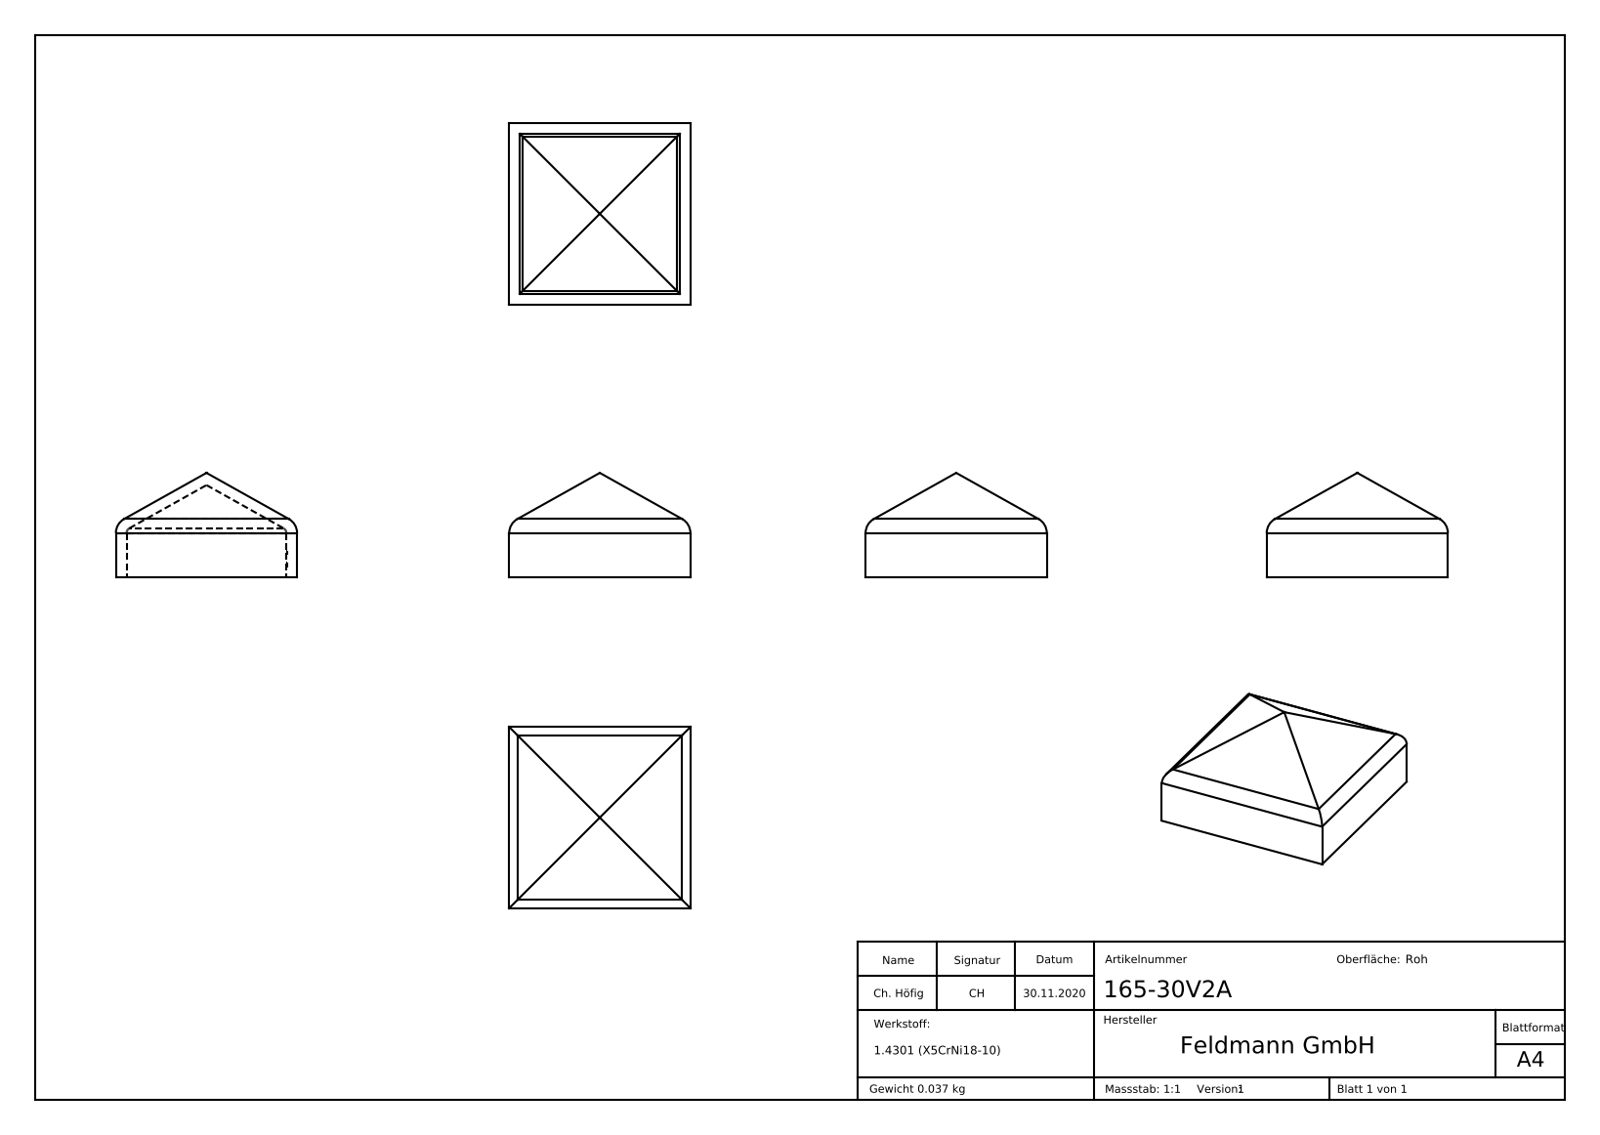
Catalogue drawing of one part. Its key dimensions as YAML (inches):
part_name: "165-30V2A"
step_written_by: "SolidWorks 2018 (CONFIG_CONTROL_DESIGN)"
units: inches
bodies: {solids: 1, faces: 246, planar: 140, cylindrical: 12, other: 94}
overall_size: [1.339, 1.339, 0.768]
volume: 0.287
surface_area: 7.711
partial_cylinders:
  - {radius: 0.039, count: 4}
  - {radius: 0.118, count: 4}
  - {radius: 0.004, count: 2}
face_to_face_distances: [0.079, 1.26, 1.339, 1.181, 0.075, 1.185, 1.264, 0.07, 0.033, 0.046]
